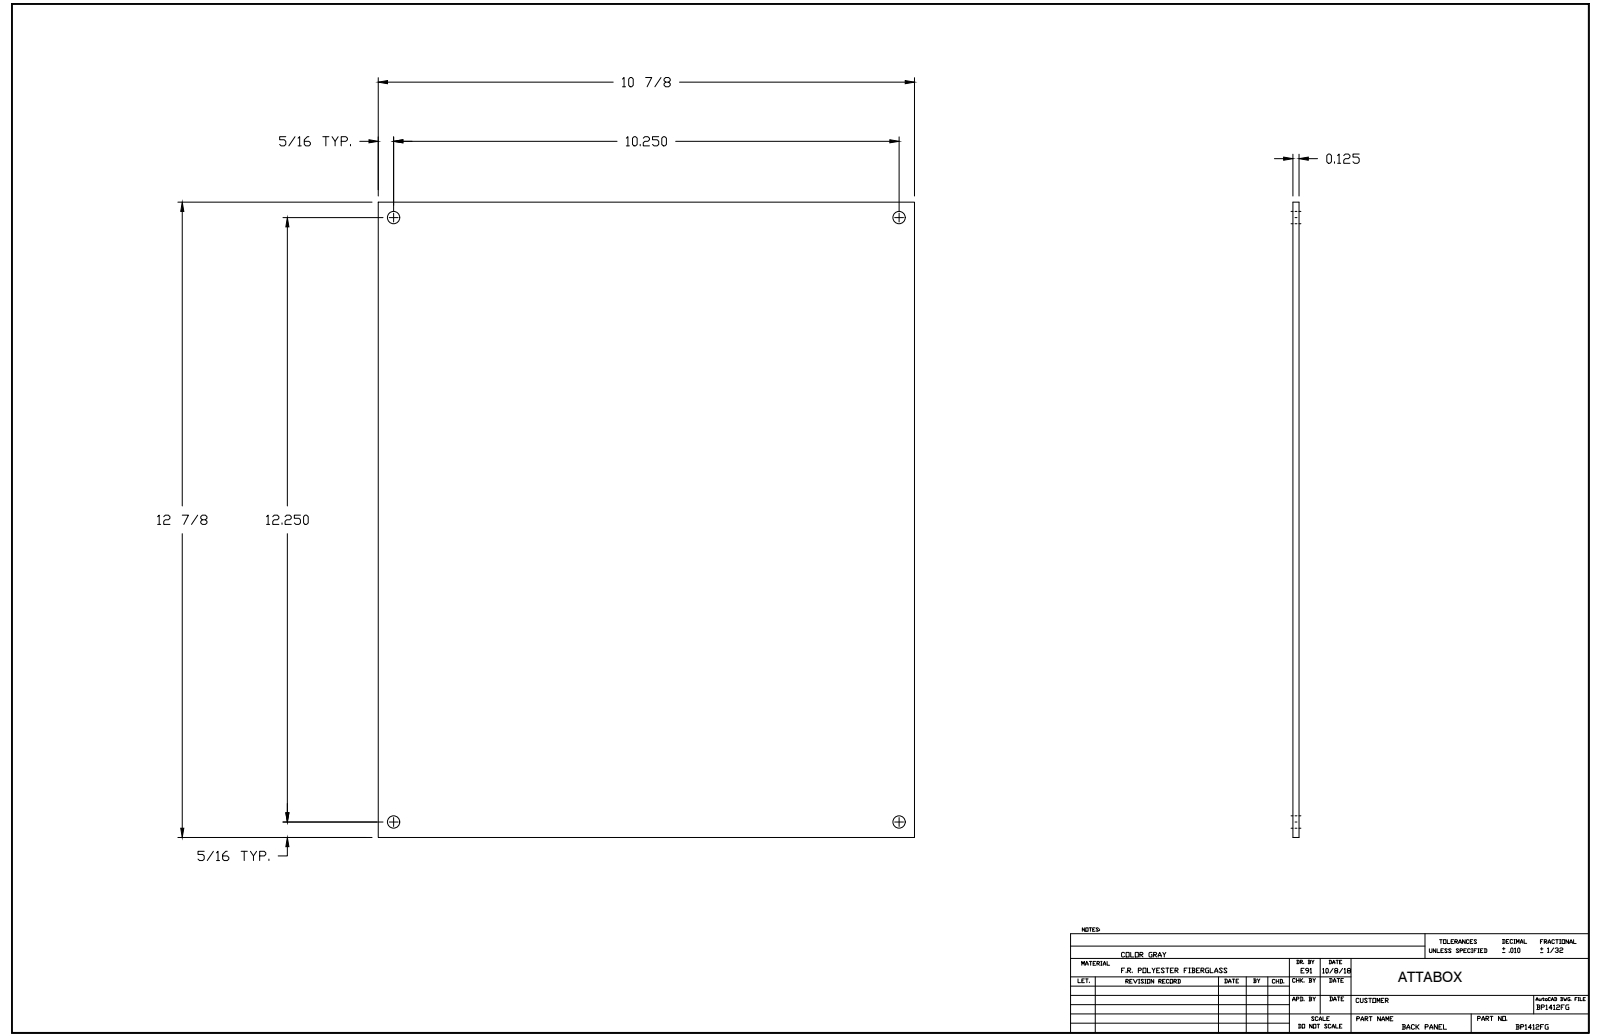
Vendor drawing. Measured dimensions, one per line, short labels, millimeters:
name: BP1412FG_STP
written by: Autodesk Inventor 2014 (AUTOMOTIVE_DESIGN)
unit: mm
bodies: 1 solid, 10 faces (6 planar, 4 cylindrical, 0 other)
size: 327.02 × 276.23 × 3.17
volume: 286 403 mm³; area: 184 496 mm²
holes: 4× ⌀6.35
face distances: 3.17, 276.22, 327.02
hole spacings: 260.34, 311.14, 405.69
